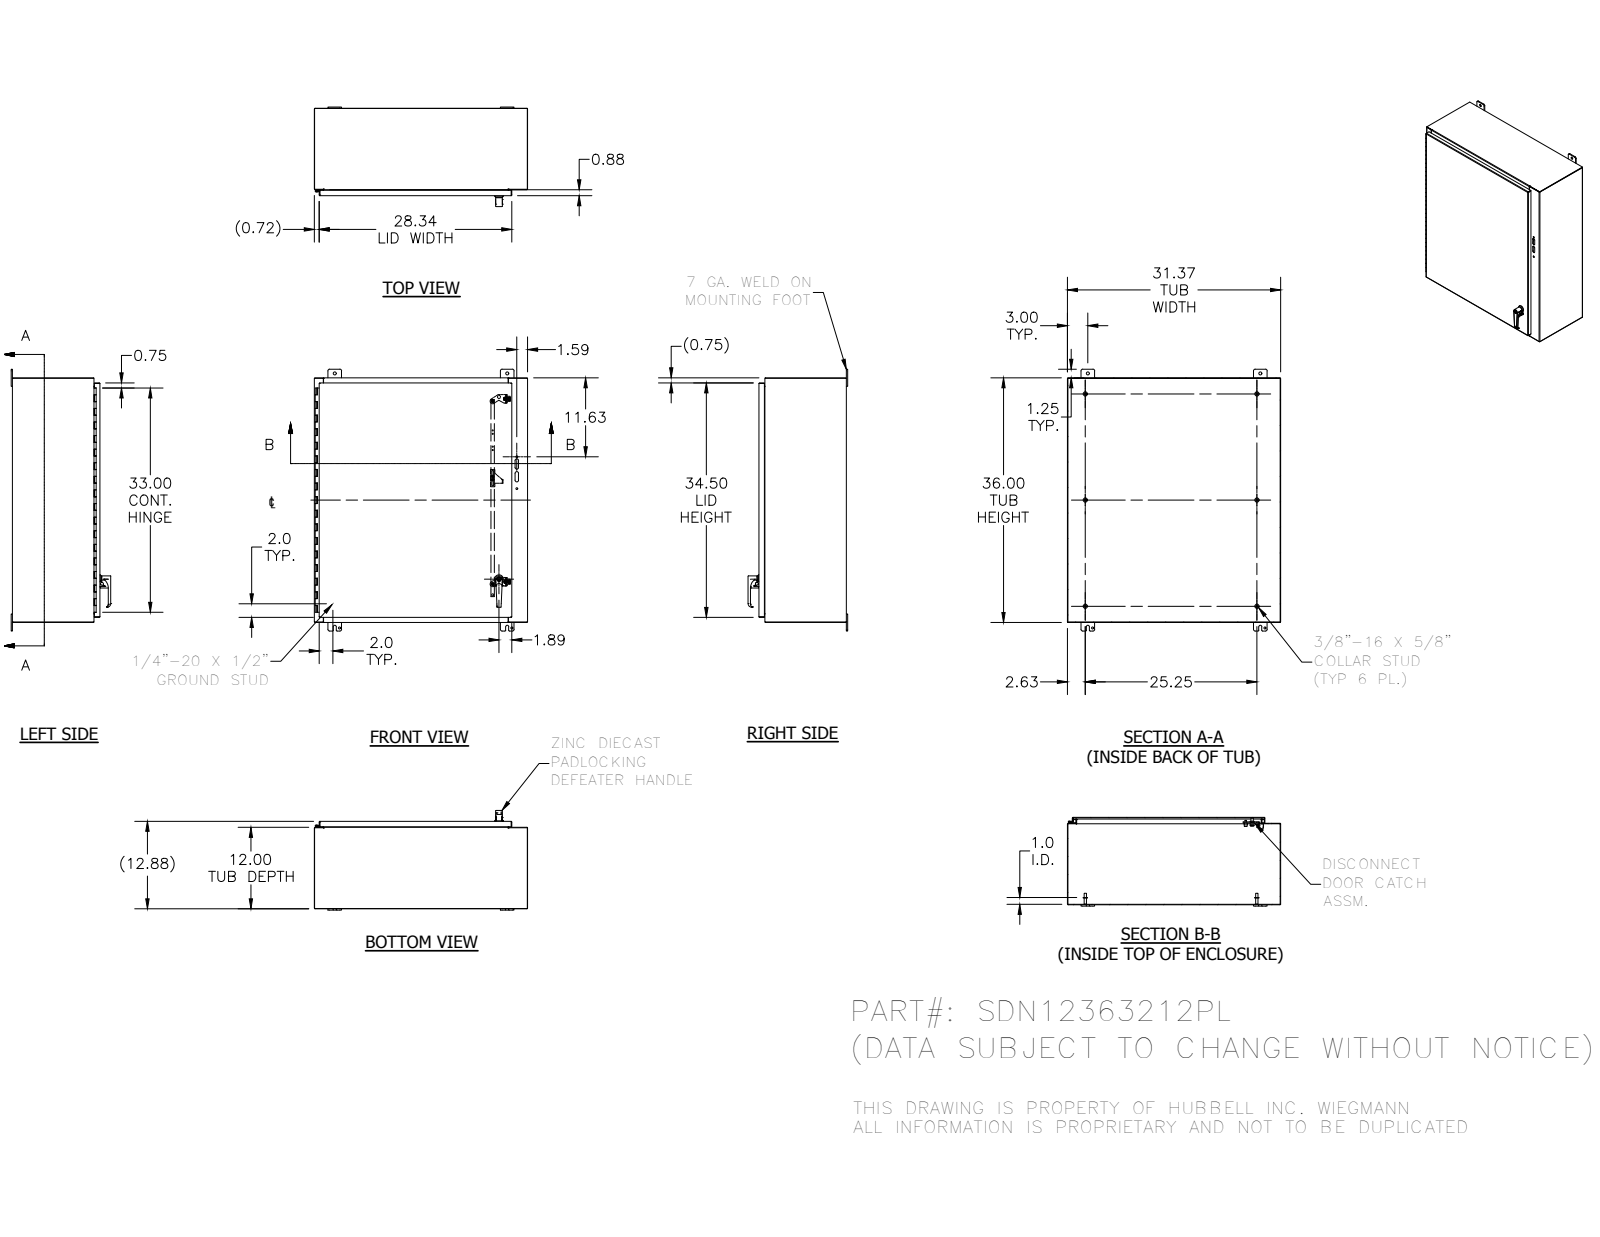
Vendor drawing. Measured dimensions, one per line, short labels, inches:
name: SDN12363212PL; SDN12363212PLBLR; 3889; 34840 (+8 more)
written by: Autodesk Inventor 2012 (AUTOMOTIVE_DESIGN)
unit: in
bodies: 53 solids, 1590 faces (848 planar, 523 cylindrical, 219 other)
size: 38.5 × 31.375 × 14.649
volume: 319.9 in³; area: 8 581 in²
holes: 6× ⌀0.145, 4× ⌀0.313, 4× ⌀0.438, 3× ⌀0.32, 2× ⌀0.156, 2× ⌀0.196, 2× ⌀0.211, 2× ⌀0.22, 2× ⌀0.281, 2× ⌀0.313, 2× ⌀0.45, 1× ⌀0.102
bosses: 7× ⌀0.625, 7× ⌀0.33, 4× ⌀0.437, 4× ⌀0.3, 4× ⌀0.25, 4× ⌀0.225, 4× ⌀0.19, 2× ⌀0.75
rounds: 38× R0.02, 30× R0.012, 22× R0.25, 18× R0.031, 18× R0.105, 16× R0.025, 15× R0.125, 6× R0.094
face distances: 0.074, 12.801, 12.727, 12.875, 31.301, 35.926, 31.227, 31.375, 11.926, 0.875
hole spacings: 26.9, 1.593, 25.375, 36, 44.044, 0.5, 2.375, 4.38
